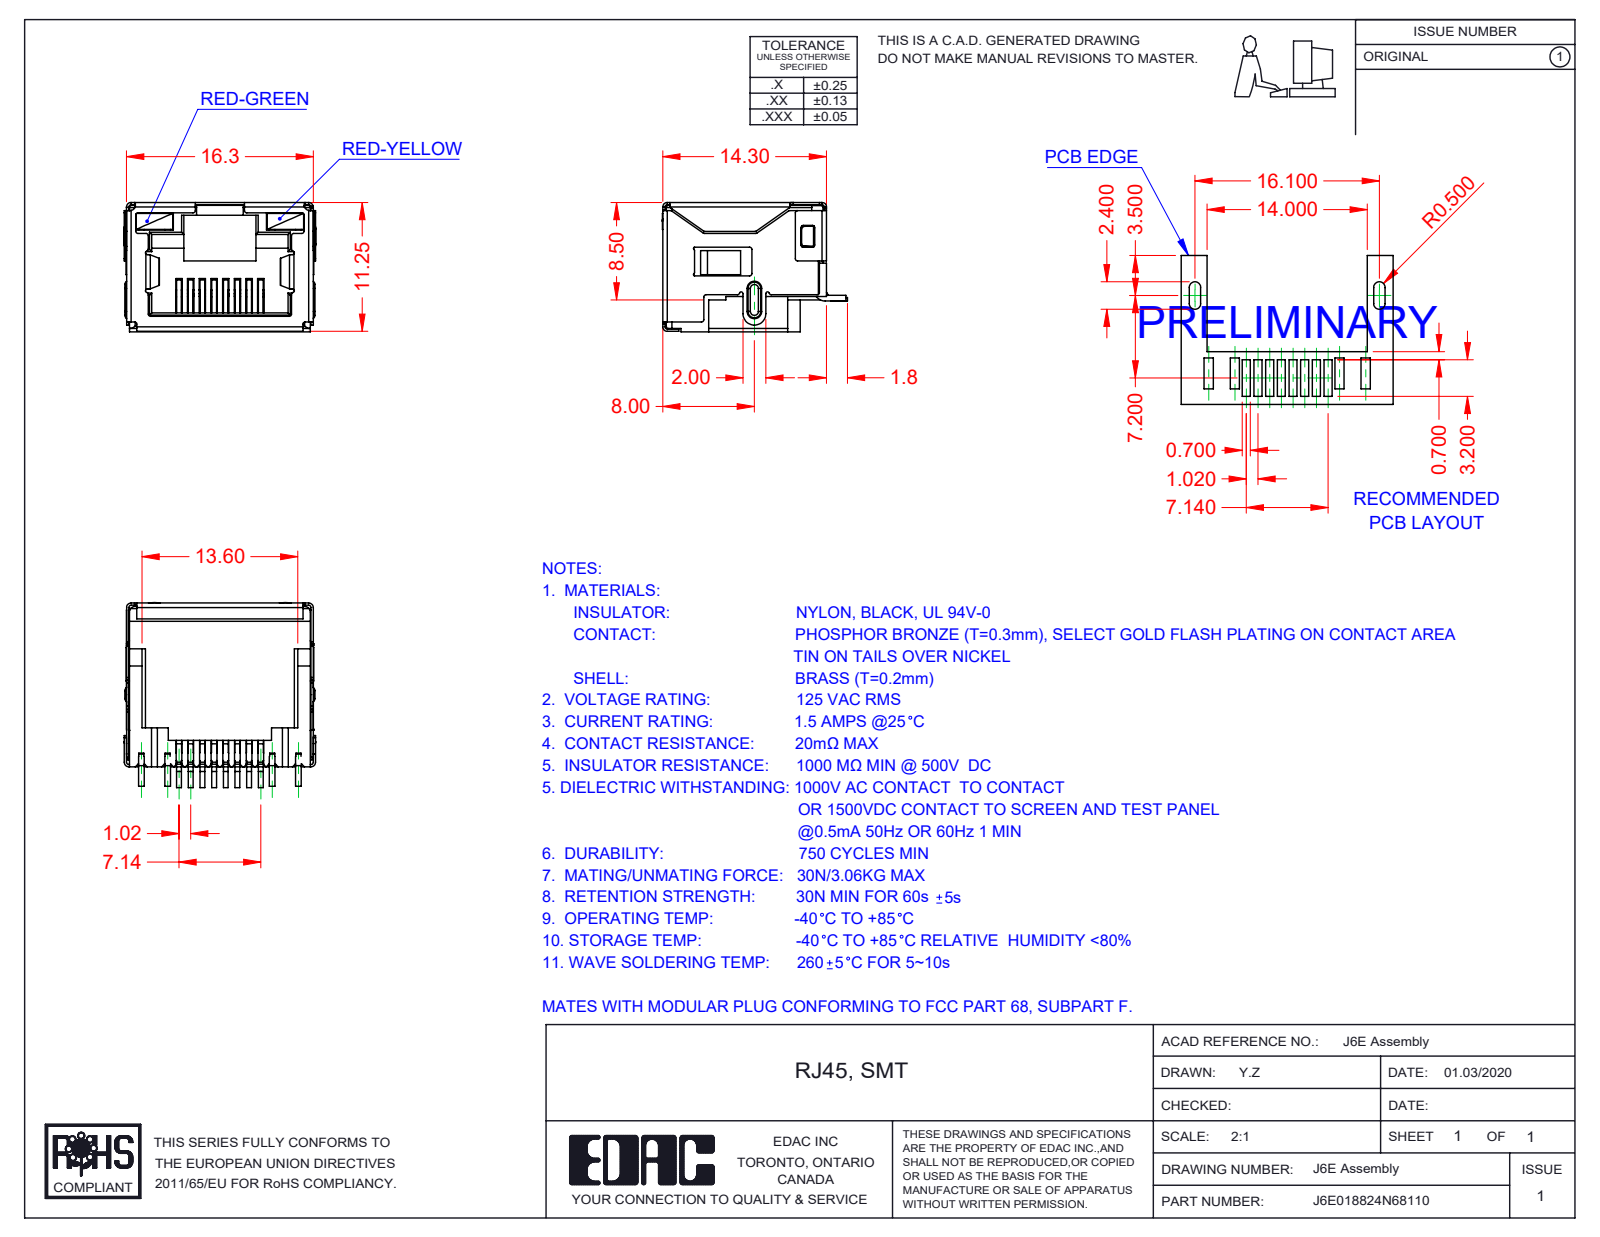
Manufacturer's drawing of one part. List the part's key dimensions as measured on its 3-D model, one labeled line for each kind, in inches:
Part name (STEP PRODUCT): 6E Contacts; 6E Insulator_LED; 6E LED RH_8-Red-Yellow; J6E018824N68110 (+2 more)
STEP written by: SolidWorks 2016 (CONFIG_CONTROL_DESIGN)
Units: inches
Bodies: 12 solids, 1500 faces (1099 planar, 351 cylindrical, 50 other)
Overall size (bounding box): 0.659 × 0.636 × 0.445
Volume: 0.068 in³ · Surface area: 6.27 in²
Partial cylindrical surfaces — rounded edges, fillets, slot ends (radius × count): R0.008 ×82, R0.01 ×17, R0.016 ×13, R0.02 ×13, R0.004 ×10, R0.006 ×7, R0.012 ×4, R0.039 ×3
Main face-to-face distances: 0.435, 0.632, 0.634, 0.624, 0.437, 0.445, 0.094, 0.028, 0.388, 0.019
